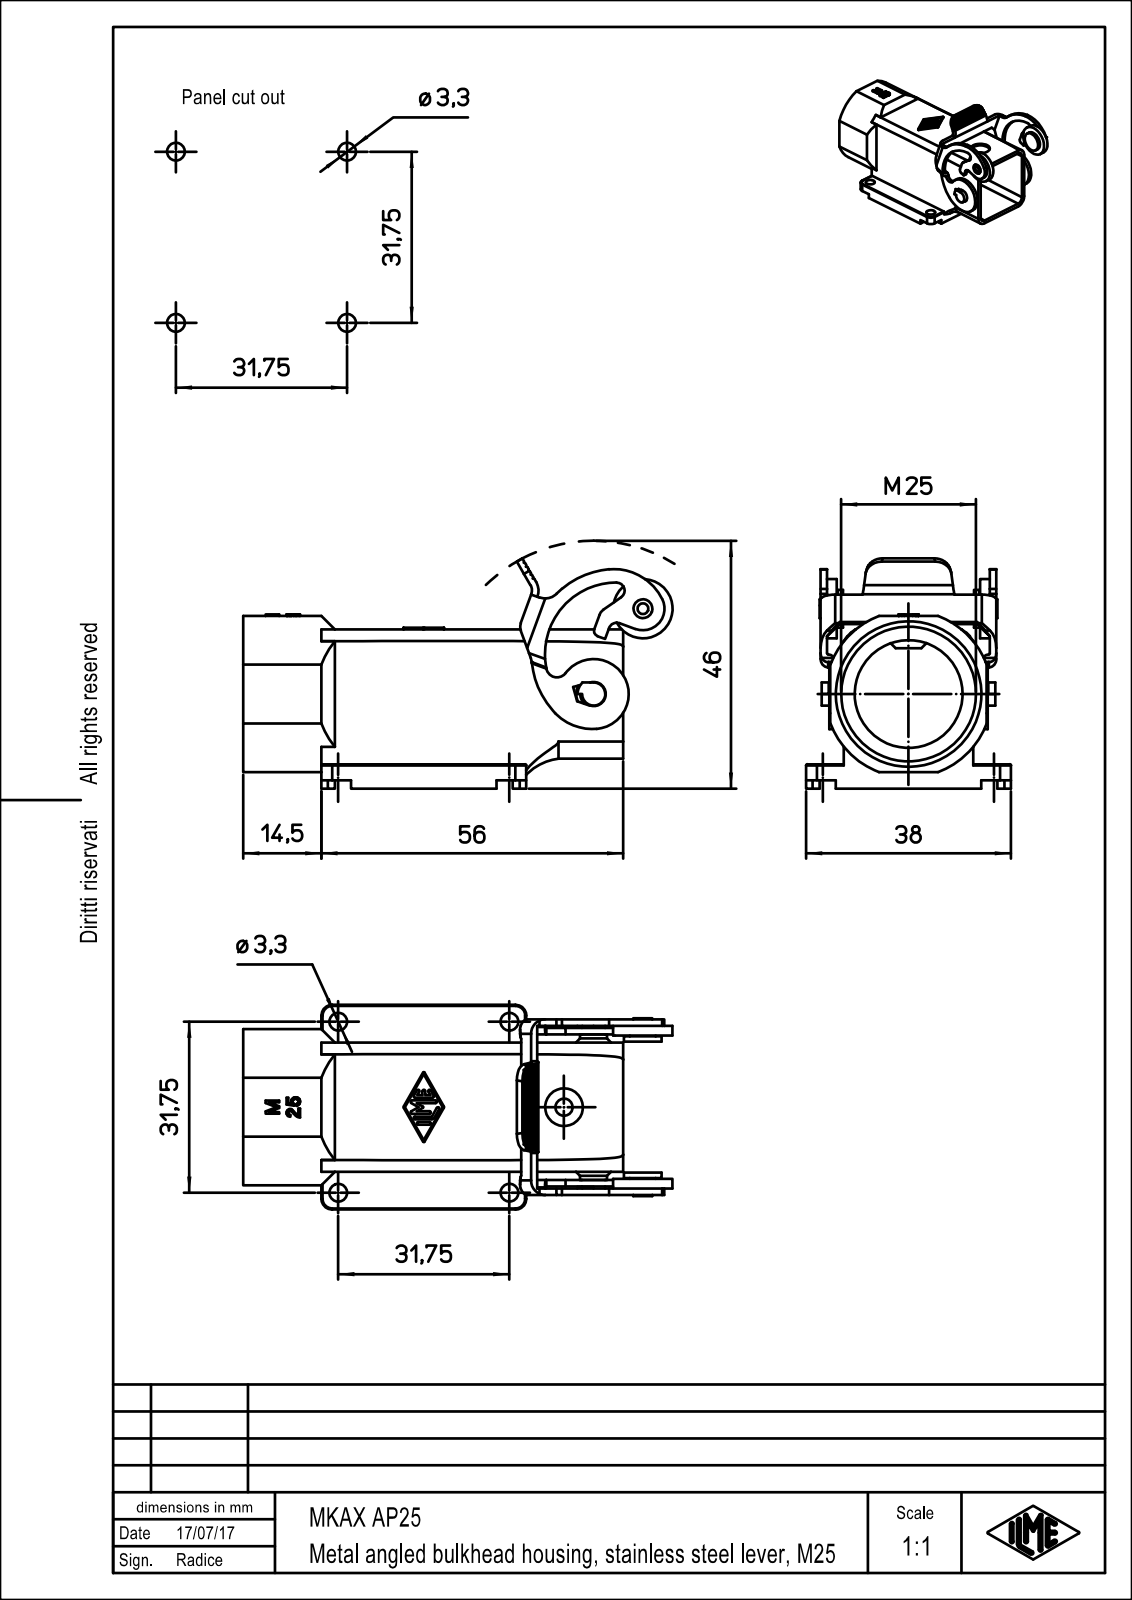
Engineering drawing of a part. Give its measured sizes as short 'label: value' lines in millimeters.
name: MKAX_AP25
written by: PTC Creo Elements/Direct Modeling 19.0E 27-Jun-2016 (C) Parametric Technology GmbH (AUTOMOTIVE_DESIGN)
unit: mm
bodies: 1 solid, 470 faces (299 planar, 150 cylindrical, 21 other)
size: 79.63 × 42.75 × 38
volume: 16 440 mm³; area: 18 510 mm²
holes: 4× ⌀3.3, 1× ⌀2, 1× ⌀3.2, 1× ⌀5, 1× ⌀7, 1× ⌀20, 1× ⌀25
bosses: 1× ⌀11, 1× ⌀7, 1× ⌀5, 1× ⌀4.8, 1× ⌀4.3, 1× ⌀3.5
rounds: 20× R2, 15× R0.25, 8× R0.2, 7× R3.2, 5× R3, 4× R1.4, 3× R0.12, 2× R1.5
face distances: 1.2, 22.8, 24, 21.6, 28, 2.7, 4.3, 29.8, 2.5, 5.5
hole spacings: 31.75, 44.79, 44.9, 18.83, 18.84
